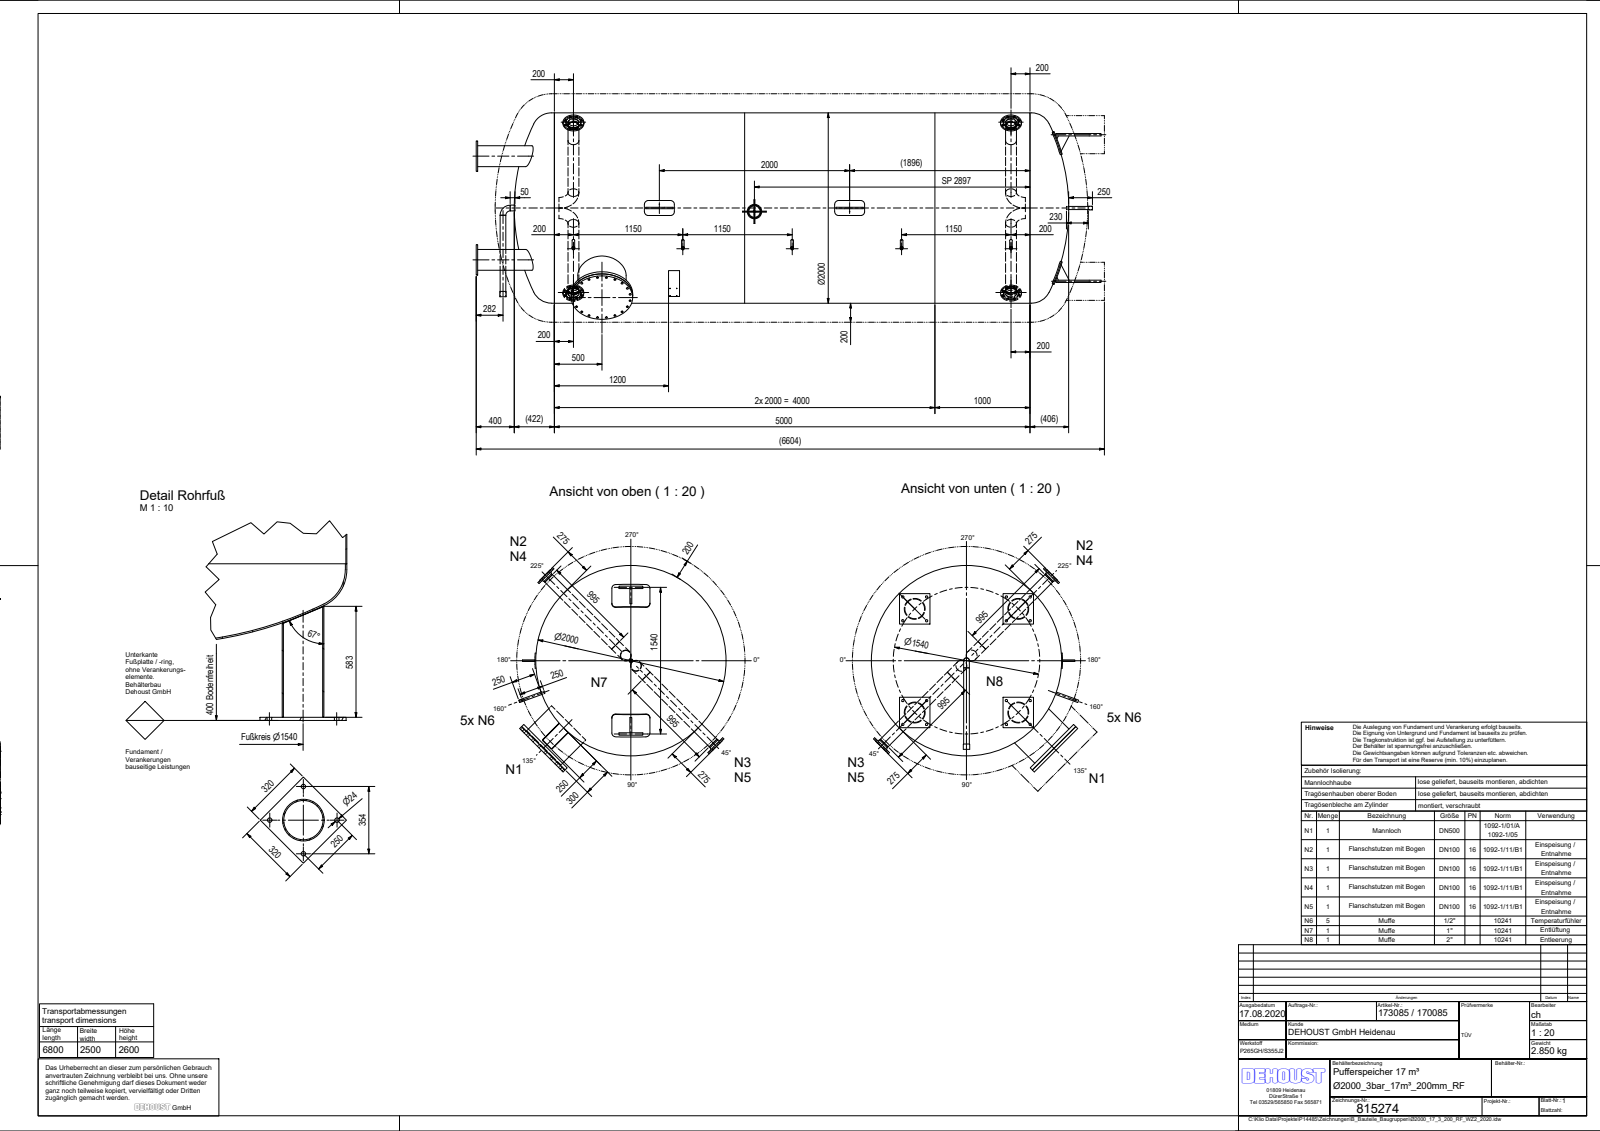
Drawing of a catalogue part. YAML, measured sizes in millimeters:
part_name: "Ø2000_17_3_200_RF_WZ2_2020; Klöpper_Gew_Ø2000_4,3; Klöpper_Gew_Ø2000_7,8; Zyl_Ø2000_5x5000_2020 (+8 more)"
step_written_by: "Autodesk Inventor 2019 (AUTOMOTIVE_DESIGN)"
units: millimeters
bodies: {solids: 54, faces: 429, planar: 182, cylindrical: 221, other: 26}
overall_size: [6569.29, 2179.13, 2169.2]
volume: 346400000
surface_area: 91990000
round_holes:
  - {diameter: 18, count: 32}
  - {diameter: 22, count: 32}
  - {diameter: 24, count: 16}
  - {diameter: 18.63, count: 5}
  - {diameter: 21.7, count: 5}
  - {diameter: 26.9, count: 5}
  - {diameter: 5.8, count: 4}
  - {diameter: 106.3, count: 4}
  - {diameter: 107.1, count: 4}
  - {diameter: 114.3, count: 4}
  - {diameter: 206.5, count: 4}
  - {diameter: 5, count: 2}
round_bosses_or_shafts:
  - {diameter: 26.9, count: 5}
  - {diameter: 26.4, count: 5}
  - {diameter: 220, count: 4}
  - {diameter: 219.1, count: 4}
  - {diameter: 158, count: 4}
  - {diameter: 114.3, count: 4}
  - {diameter: 645, count: 2}
  - {diameter: 2000, count: 1}
partial_cylinders:
  - {radius: 42, count: 16}
  - {radius: 10, count: 6}
  - {radius: 6, count: 4}
  - {radius: 5, count: 2}
  - {radius: 36, count: 2}
  - {radius: 72, count: 2}
  - {radius: 125, count: 1}
  - {radius: 1009, count: 1}
face_to_face_distances: [400, 16, 28, 25, 557.5, 957.5, 582.5, 982.5, 1540, 3217.45]
hole_center_spacings: [90, 300, 4600, 93.86, 185.41, 352.67, 1150, 592.61]
